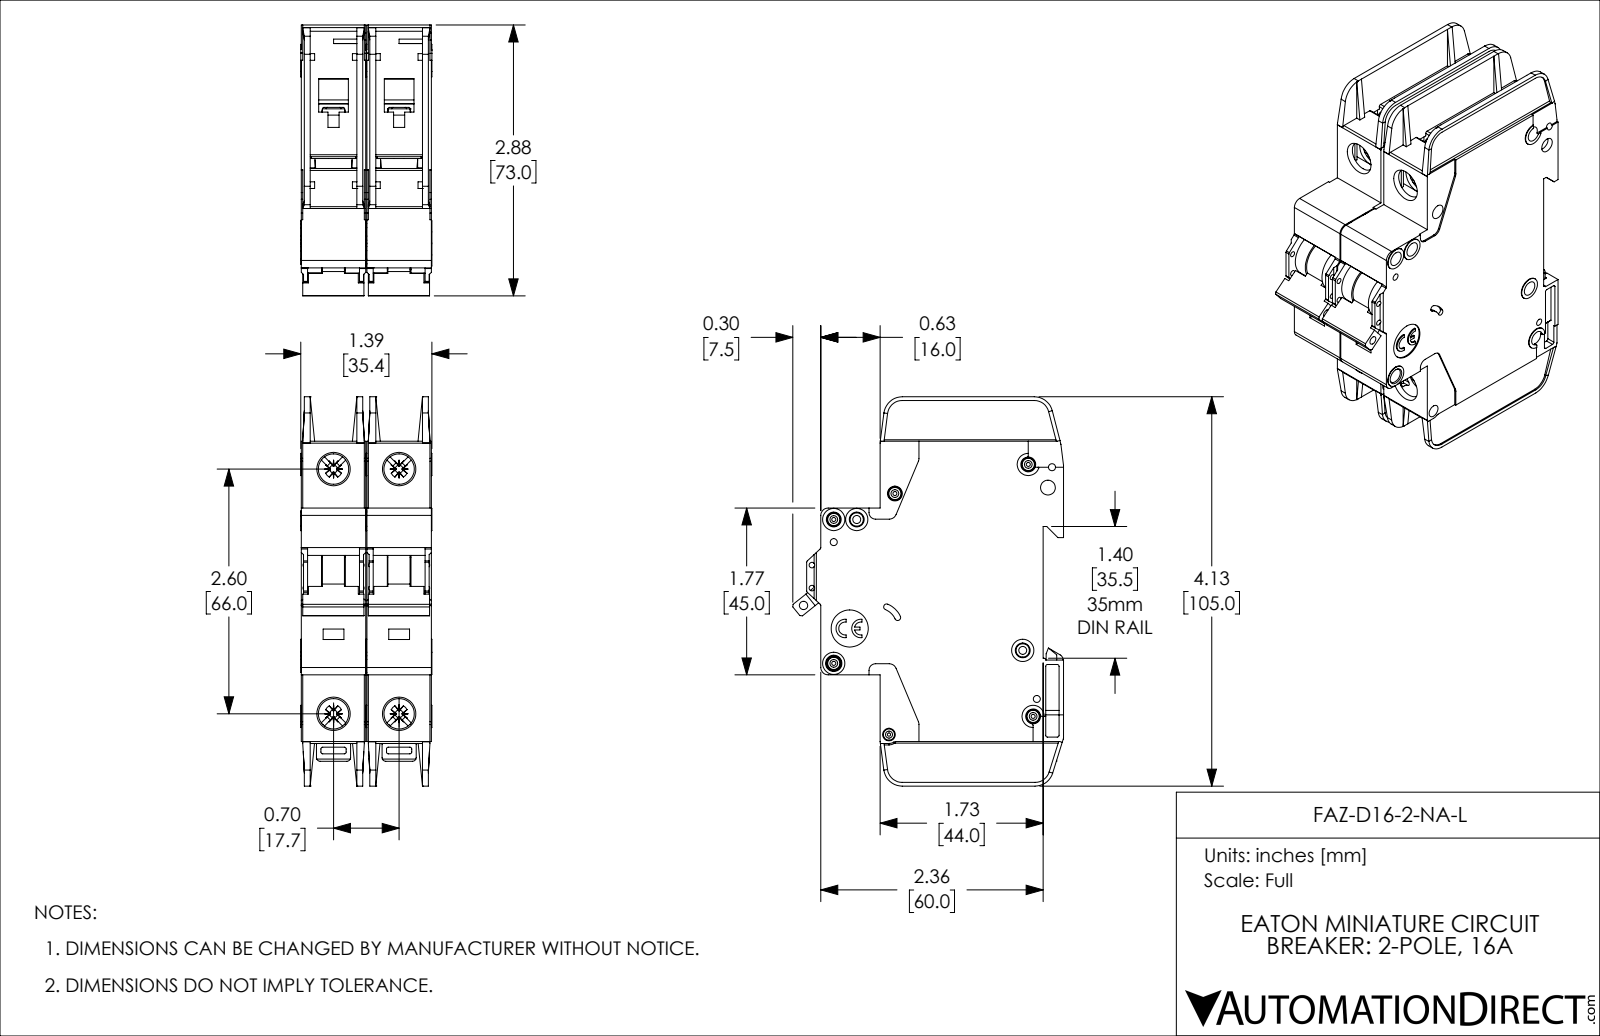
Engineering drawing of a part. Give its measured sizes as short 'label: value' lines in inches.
name: FAZ-D16-2-NA-L
written by: SolidWorks 2019 (AUTOMOTIVE_DESIGN)
unit: in
bodies: 2 solids, 2254 faces (1342 planar, 714 cylindrical, 198 other)
size: 4.134 × 2.876 × 1.394
volume: 9.365 in³; area: 82.01 in²
holes: 8× ⌀0.157, 5× ⌀0.043, 4× ⌀0.075, 4× ⌀0.323, 2× ⌀0.059, 2× ⌀0.085, 1× ⌀0.035, 1× ⌀0.089, 1× ⌀0.098, 1× ⌀0.134, 1× ⌀0.394
bosses: 5× ⌀0.13, 4× ⌀0.236, 3× ⌀0.118, 2× ⌀0.098
rounds: 57× R0.02, 20× R0.016, 14× R0.039, 10× R0.079, 8× R0.043, 5× R0.008, 5× R0.197, 4× R0.01
face distances: 0.697, 0.047, 0.685, 0.591, 0.094, 0.638, 0.543, 1.382, 0.744, 0.65
hole spacings: 0.244, 0.537, 0.697, 0.87, 2.598, 2.69, 0.189, 0.199
